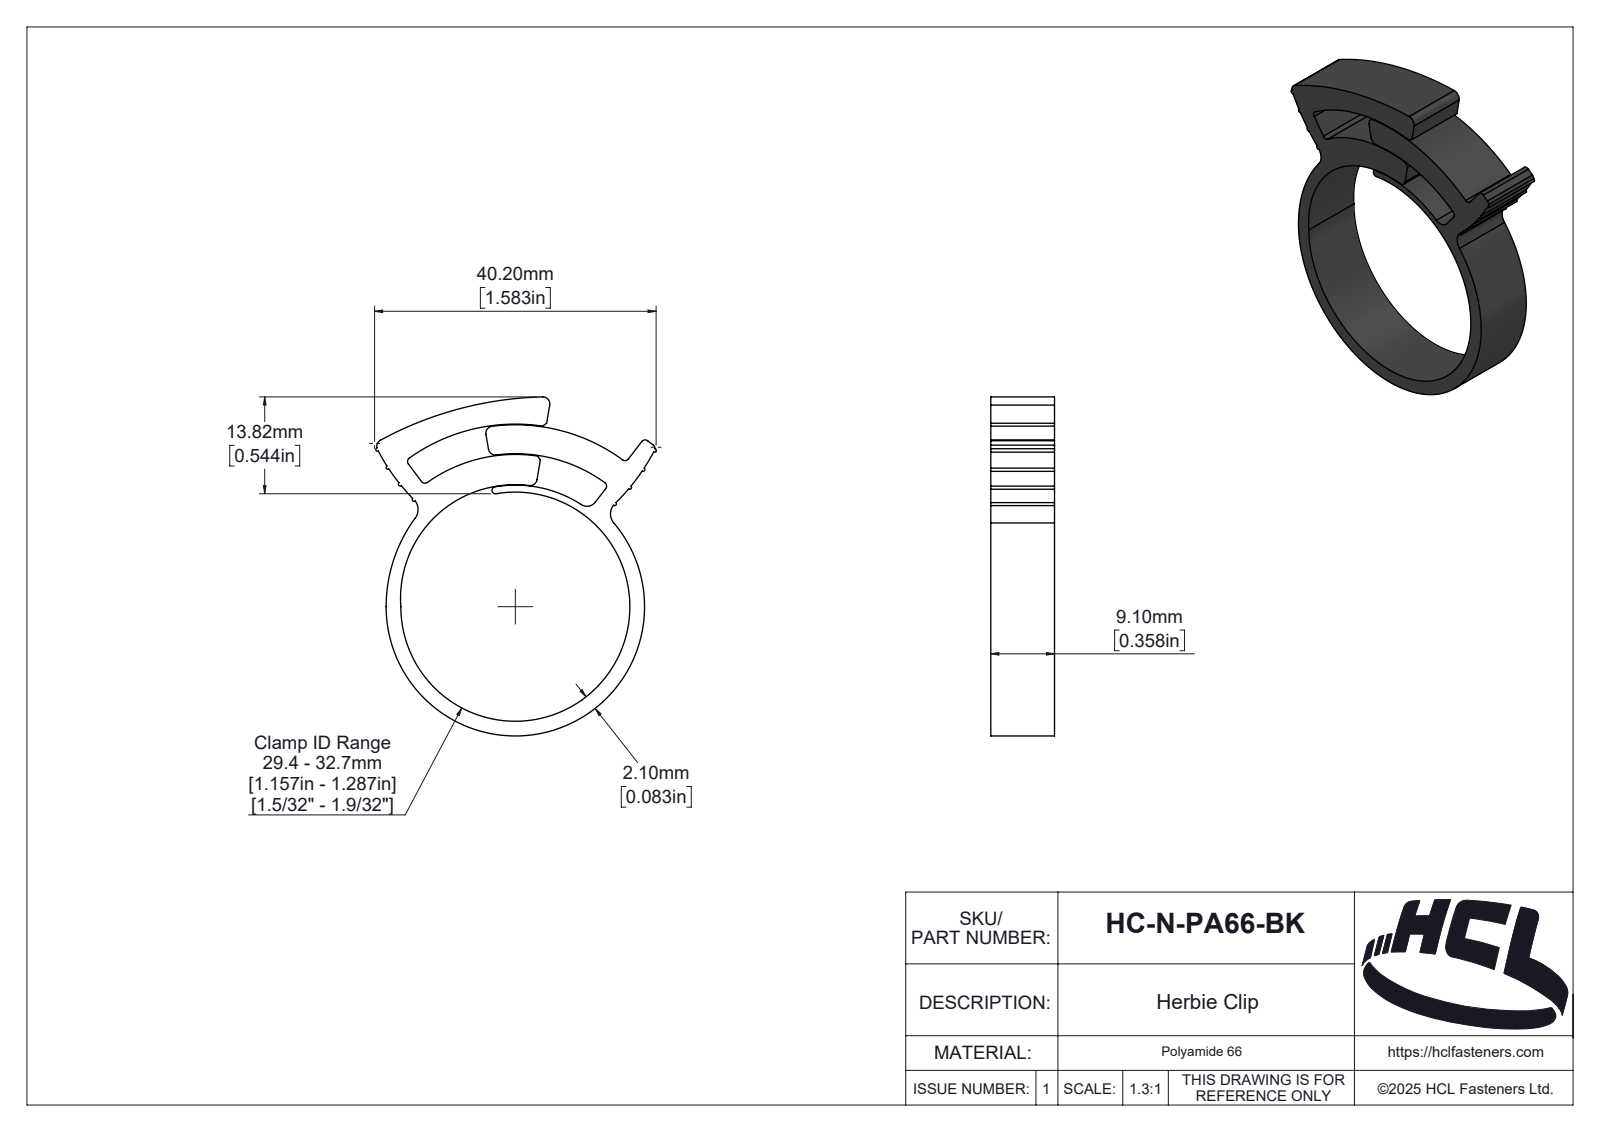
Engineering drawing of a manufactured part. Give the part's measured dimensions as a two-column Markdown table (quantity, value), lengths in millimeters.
| quantity | value |
| --- | --- |
| part name | HC-N-PA66-BK |
| STEP written by | SolidWorks 2025 (AUTOMOTIVE_DESIGN) |
| units | millimeters |
| bodies | 1 solid, 162 faces (13 planar, 100 cylindrical, 49 other) |
| overall size | 48.39 × 40.05 × 9.1 |
| volume | 4 425 mm³ |
| surface area | 4 303 mm² |
| partial cylindrical surfaces (radius × count) | 0.25 × 8, 0.6 × 6, 1 × 5, 2 × 2, 0.17 × 1, 0.5 × 1, 0.67 × 1, 0.84 × 1 |
| main face-to-face distances | 9.1 |
